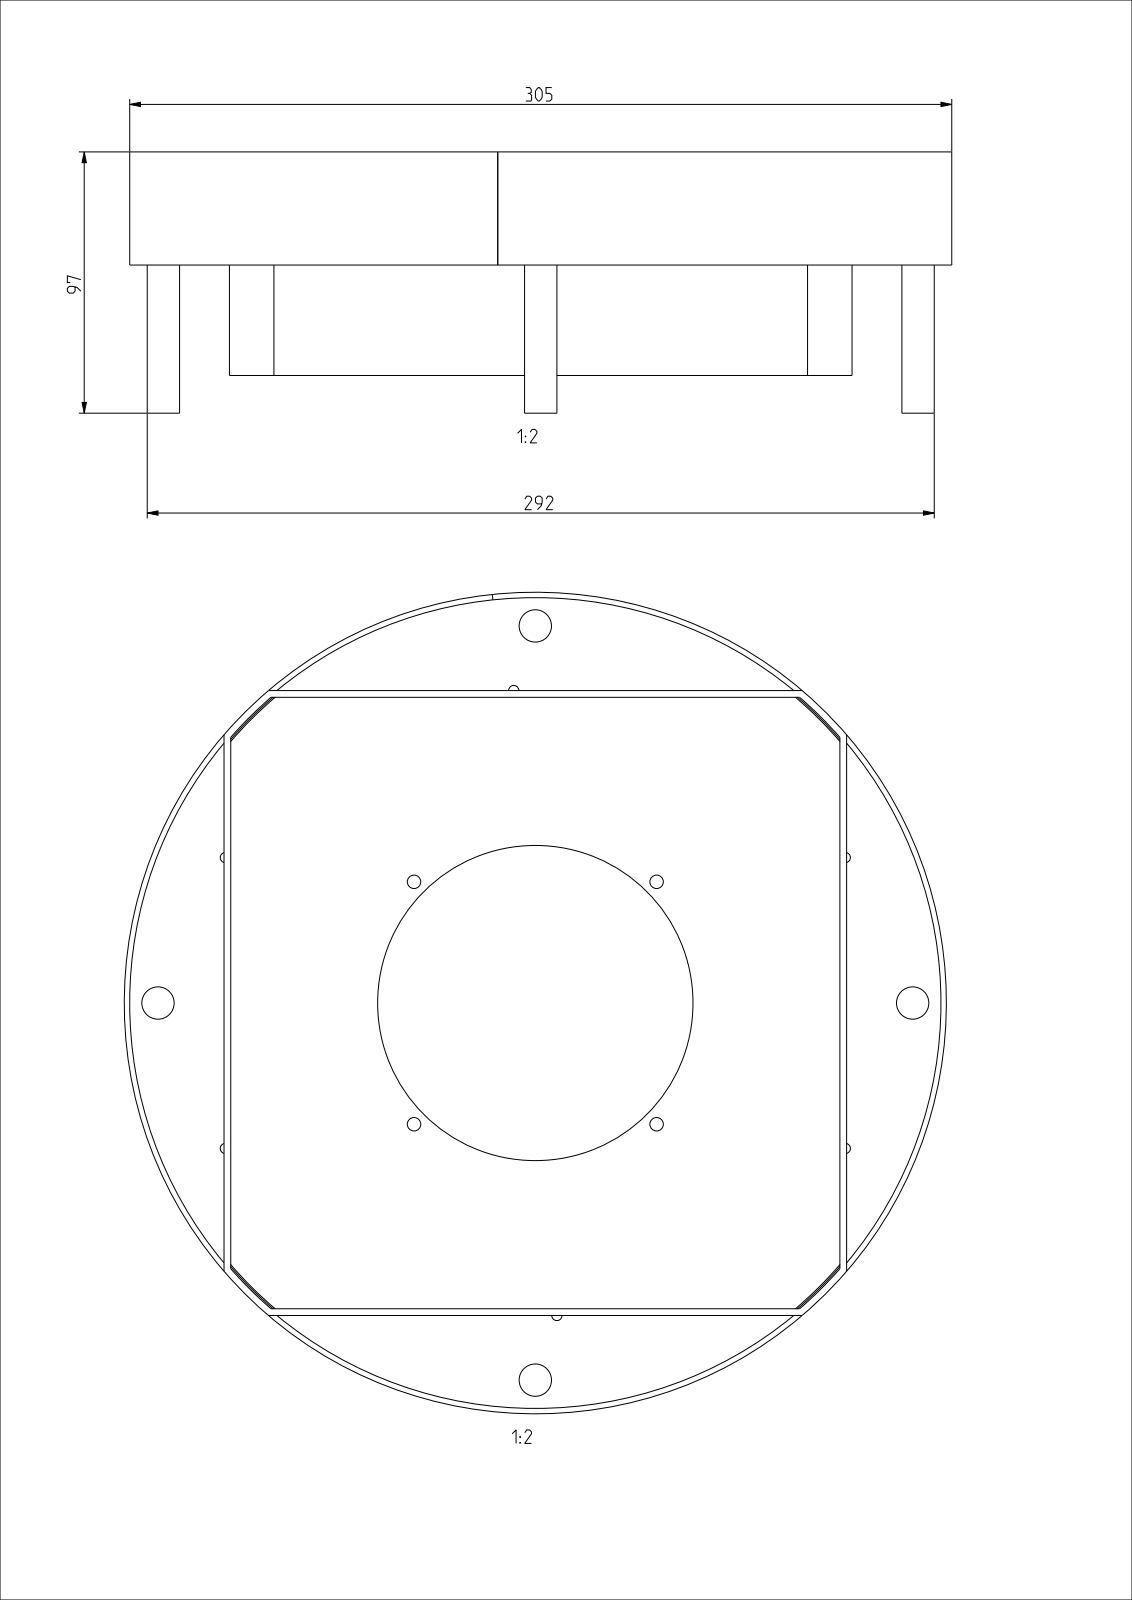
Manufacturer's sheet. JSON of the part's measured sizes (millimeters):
{"part_name": "T-00702; T-00703; T-00704; T-00711 (+8 more)", "step_written_by": "CREO PARAMETRIC BY PTC INC, 2022024 (AUTOMOTIVE_DESIGN)", "units": "millimeters", "bodies": {"solids": 9, "faces": 146, "planar": 74, "cylindrical": 72, "other": 0}, "overall_size": [305, 305, 97], "volume_mm3": 986016, "surface_area_mm2": 576089, "round_holes": [[3.8, 6], [5, 4], [10.1, 4], [117, 1]], "round_bosses_or_shafts": [[12, 4], [9.85, 4], [305, 1], [301, 1], [299, 1], [298, 1], [295, 1]], "partial_cylinders_radius": [[0.5, 8], [150, 1]], "face_to_face_distances": [2, 12, 10, 2.5, 15, 17, 5, 228.5, 3, 13], "hole_center_spacings": [105.12, 190.39, 59.51, 63.64, 70.58, 90, 121.25, 127.05]}
